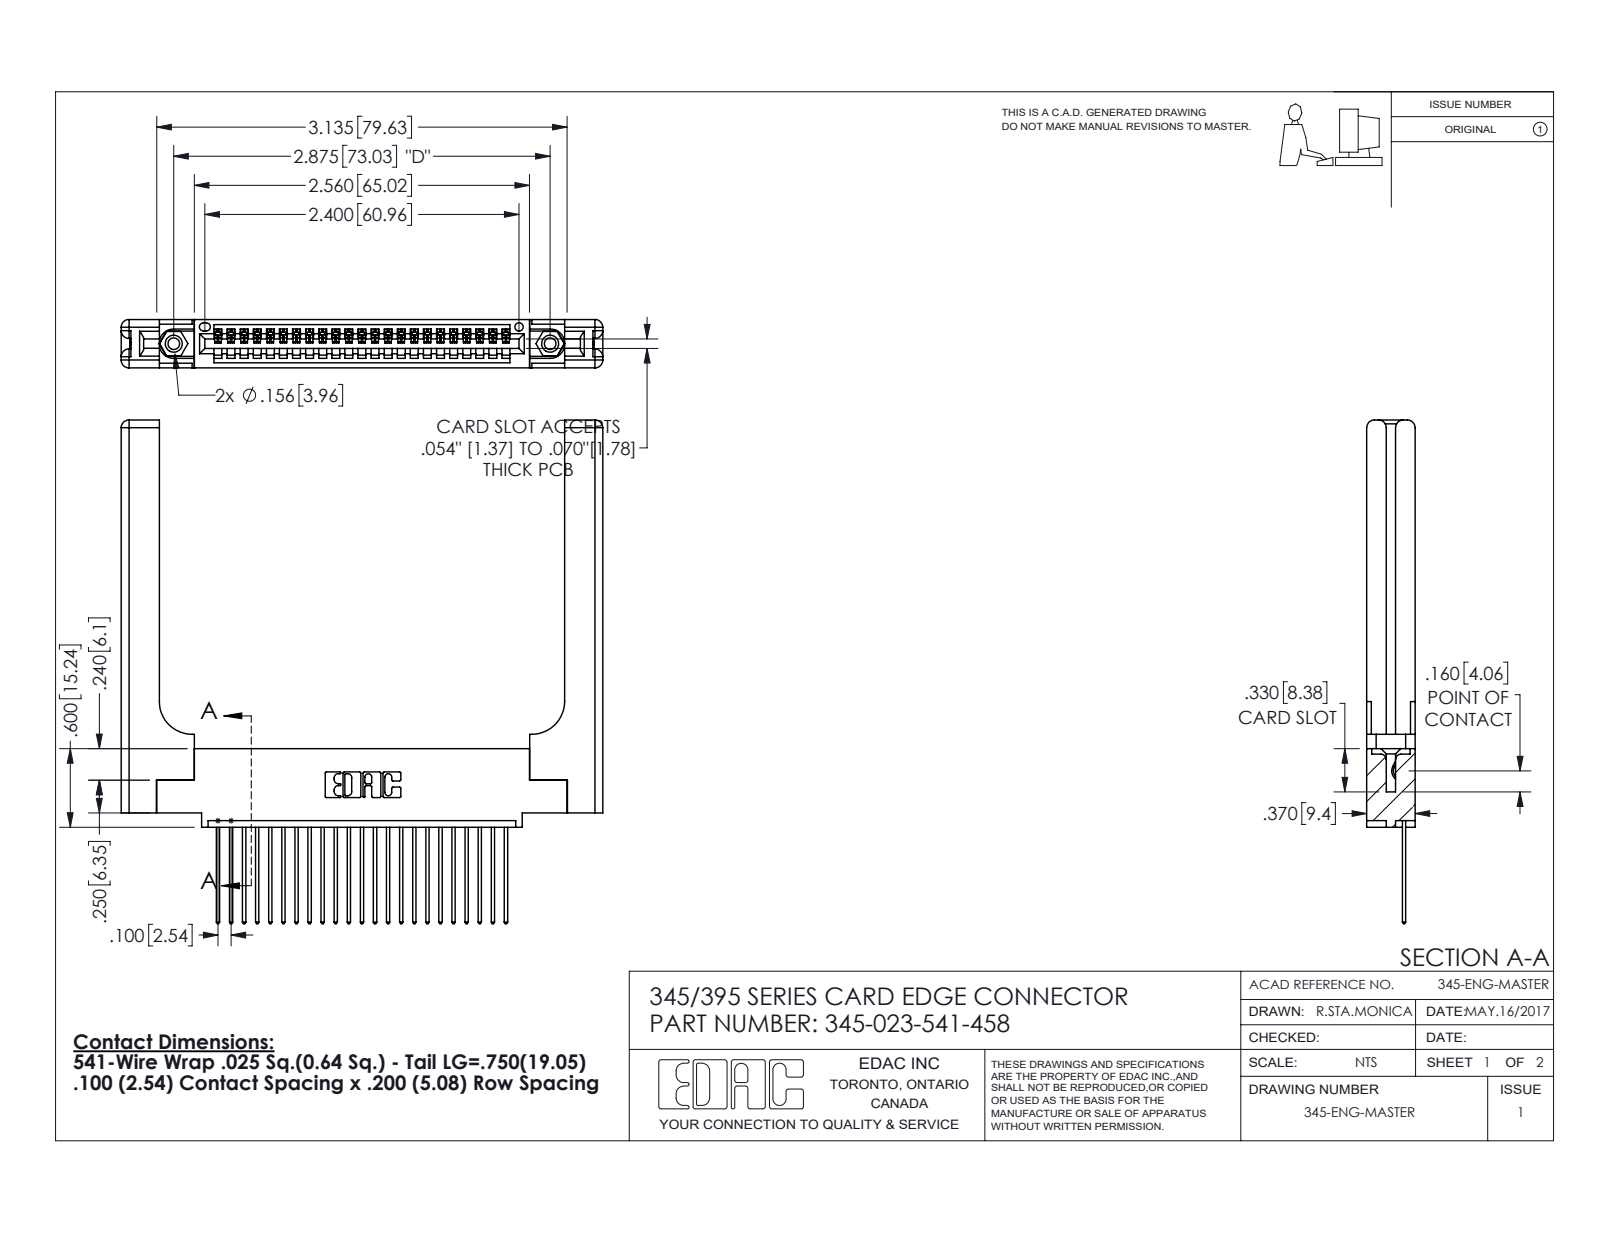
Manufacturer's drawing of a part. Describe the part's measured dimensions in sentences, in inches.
The part is named "345-023-541-458; 345 Part_0.110 Offset - 0.156 Dia-TH; 345-220-058_345-220-058; 345-250-001_345-250-001-102 (+1 more)". Its 3-D file was written by "SolidWorks 2016 (CONFIG_CONTROL_DESIGN)". It is 28 solids with 1720 faces: 1152 planar, 508 cylindrical and 60 other. Overall it measures 3.847 by 3.679 by 0.37 inches. Its volume is 1.051 cubic inches and its surface area 26.61 square inches. Round holes: 2 of diameter 0.089, 2 of diameter 0.125, 2 of diameter 0.156, 1 of diameter 0.064. Round bosses or shafts: 2 of diameter 0.155. Partial cylindrical surfaces (rounded edges, fillets, slot ends): 46 of radius 0.006, 46 of radius 0.01, 22 of radius 0.01, 16 of radius 0.06, 6 of radius 0.007, 6 of radius 0.031, 3 of radius 0.026, 2 of radius 0.03. The main face-to-face distances are 0.37, 0.072, 0.298, 0.098, 0.272, 0.025, 0.15, 0.148, 0.077, 0.2. The hole center spacings are 0.27, 2.641, 2.875.
